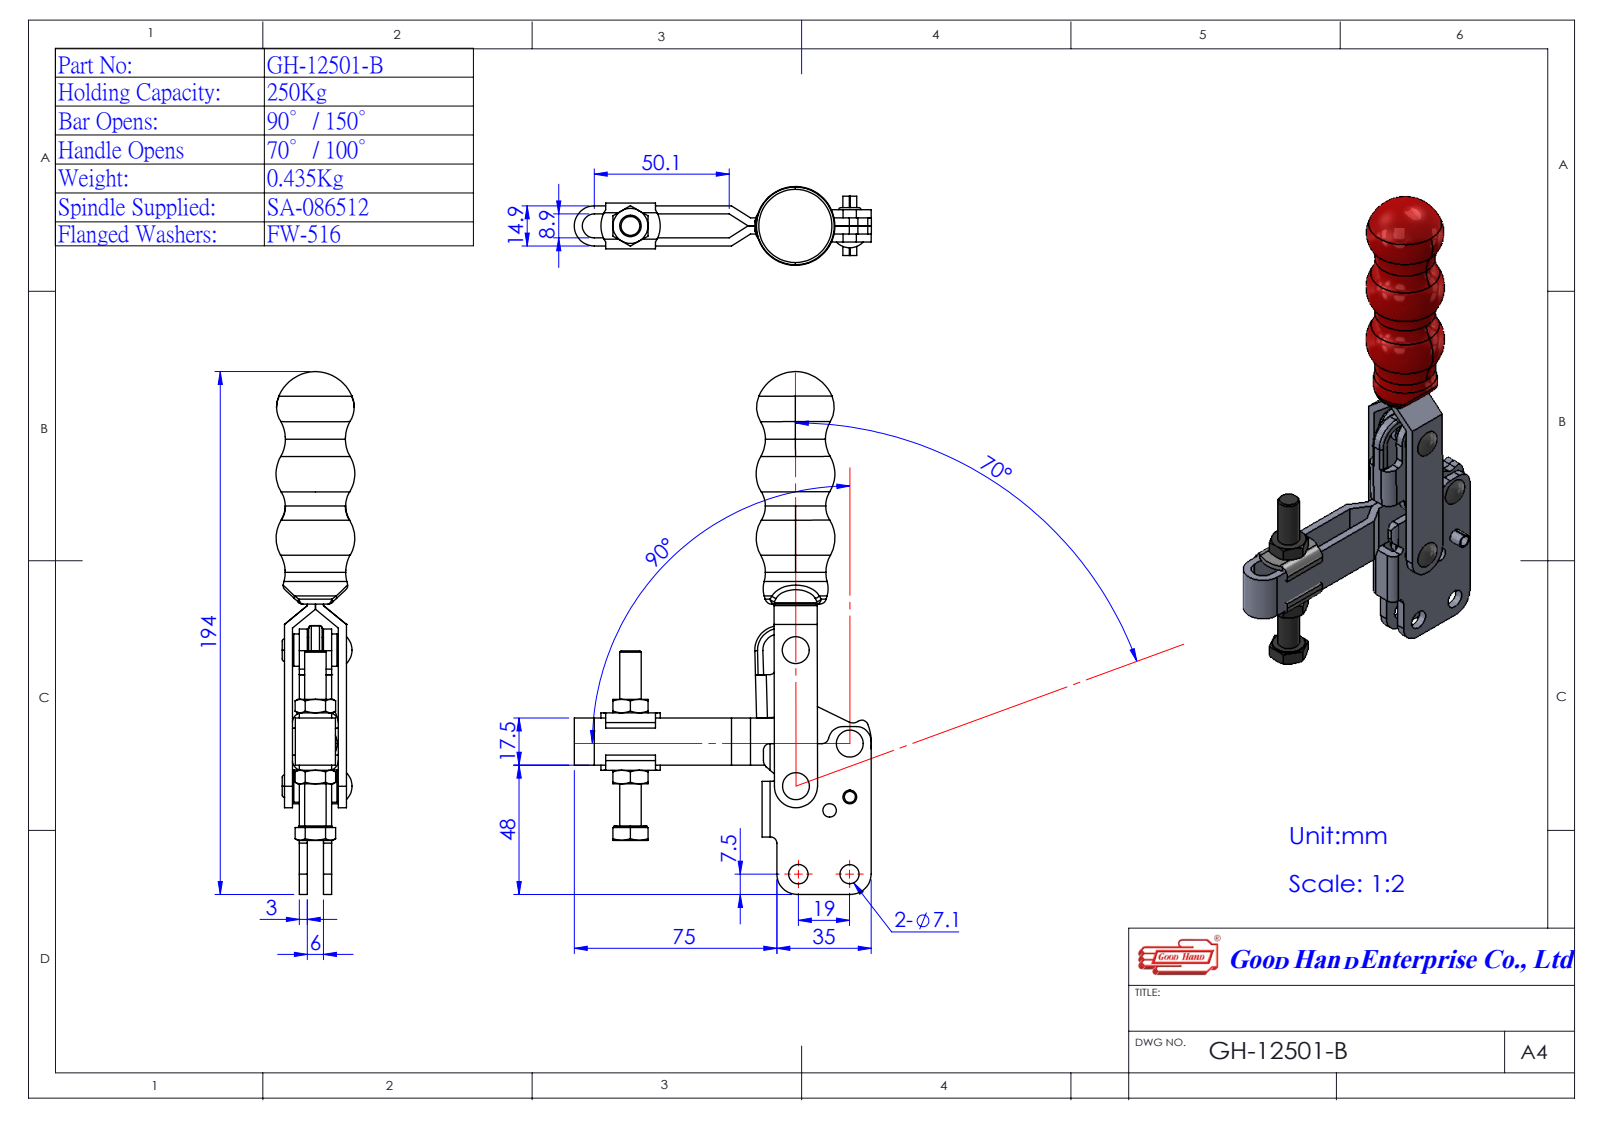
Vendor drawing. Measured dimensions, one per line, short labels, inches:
name: 112502B08-1^GH-12501-B(簡化)-1; Group1^GH-12501-B(簡化)-1; Group5^GH-12501-B(簡化)-1; GH-12501-B(簡化)-1 (+2 more)
written by: SolidWorks 2016 (AUTOMOTIVE_DESIGN)
unit: in
bodies: 5 solids, 317 faces (138 planar, 123 cylindrical, 56 other)
size: 7.427 × 4.343 × 1.028
volume: 4.642 in³; area: 60.99 in²
holes: 5× ⌀0.197, 1× ⌀0.28, 1× ⌀0.283
bosses: 2× ⌀0.394, 1× ⌀0.492, 1× ⌀0.315, 1× ⌀0.201
rounds: 6× R0.118, 4× R0.047, 4× R0.142, 3× R0.039, 2× R0.02, 2× R0.079, 2× R0.098, 2× R0.197
face distances: 0.118, 0.354, 0.217, 0.571, 0.236, 0.159, 0.057, 0.411, 0.628, 0.472
hole spacings: 0.606, 0.748, 0.833, 0.958, 0.976, 1.004, 1.02, 1.03
